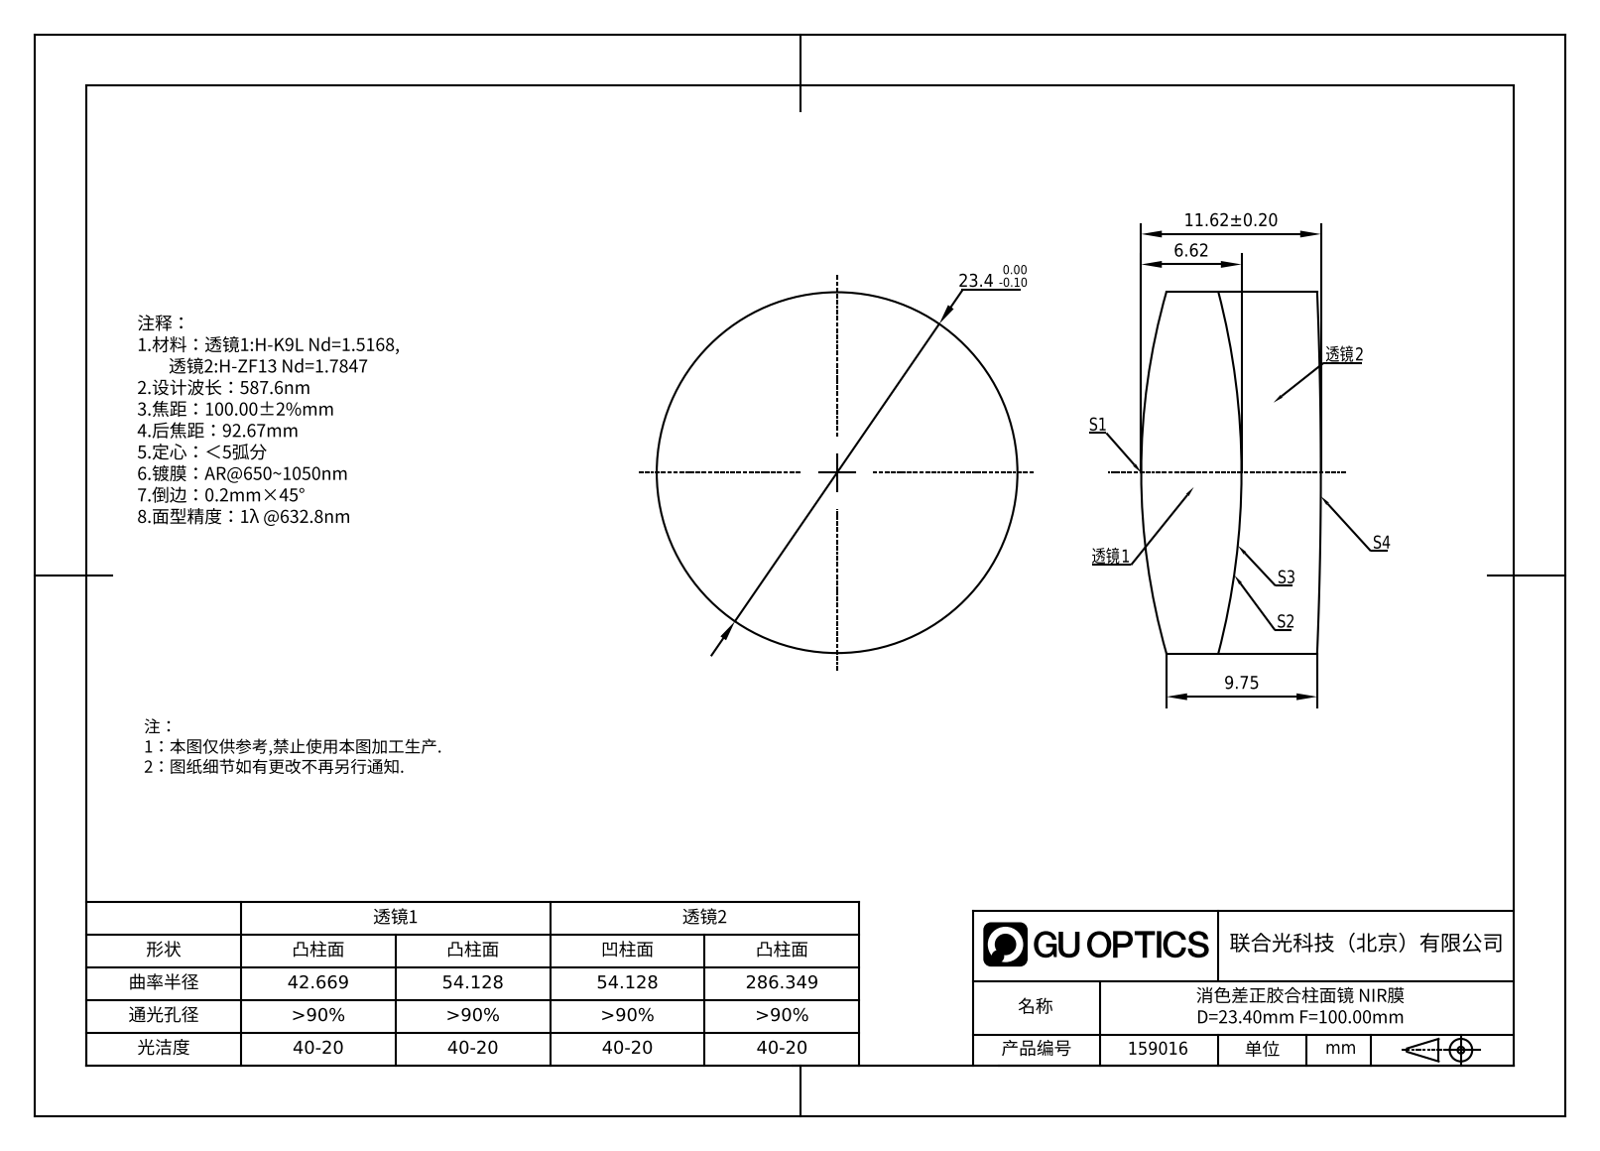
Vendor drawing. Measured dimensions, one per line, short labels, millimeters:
name: 159016
written by: SolidWorks 2020 (CONFIG_CONTROL_DESIGN)
unit: mm
bodies: 1 solid, 5 faces (0 planar, 5 cylindrical, 0 other)
size: 23.4 × 23.4 × 11.62
volume: 4 798 mm³; area: 1 650 mm²
bosses: 1× ⌀23.4
rounds: 1× R42.7, 1× R286.35
